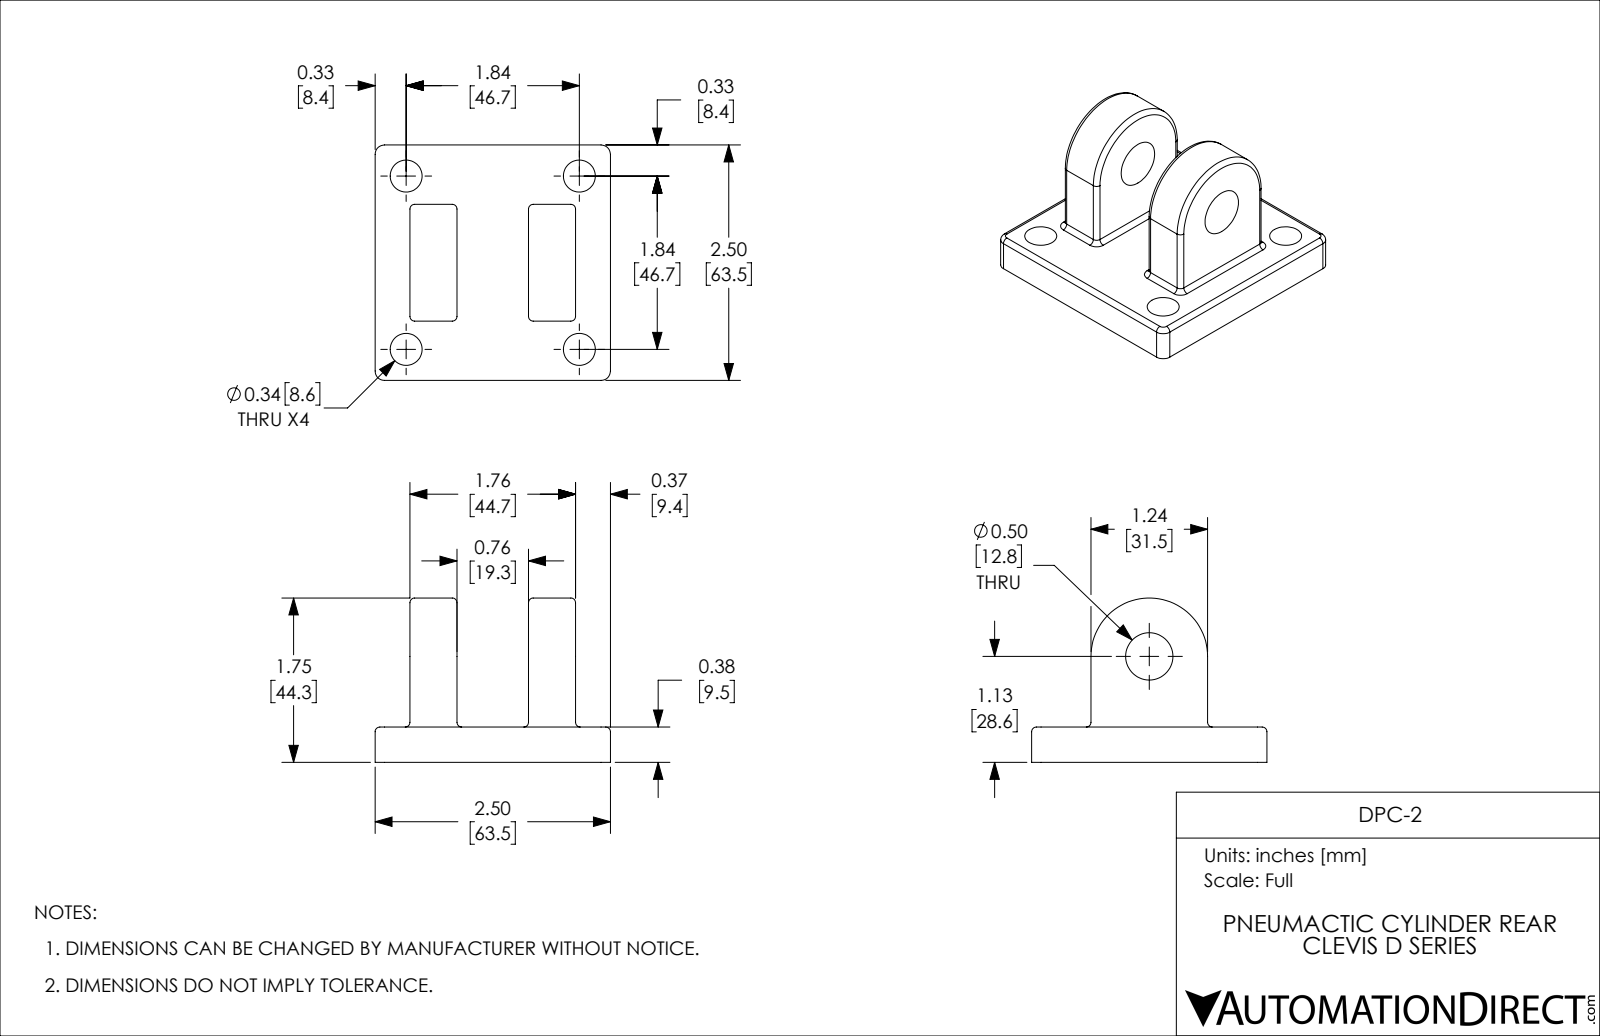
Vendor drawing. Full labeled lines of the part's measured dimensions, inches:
Part name (STEP PRODUCT): DPC-2
STEP written by: SolidWorks 2018 (AUTOMOTIVE_DESIGN)
Units: inches
Bodies: 1 solid, 71 faces (14 planar, 39 cylindrical, 18 other)
Overall size (bounding box): 2.5 × 2.5 × 1.745
Volume: 3.531 in³ · Surface area: 25.52 in²
Round holes (diameter × count): ⌀0.34 ×4, ⌀0.502 ×1
Partial cylindrical surfaces — rounded edges, fillets, slot ends (radius × count): R0.05 ×20, R0.1 ×4, R0.62 ×1
Main face-to-face distances: 0.375, 0.5, 1.26, 2.5, 0.37, 0.87, 1.63, 2.13, 0.63, 1.87
Hole centre spacings: 1.84, 2.602
